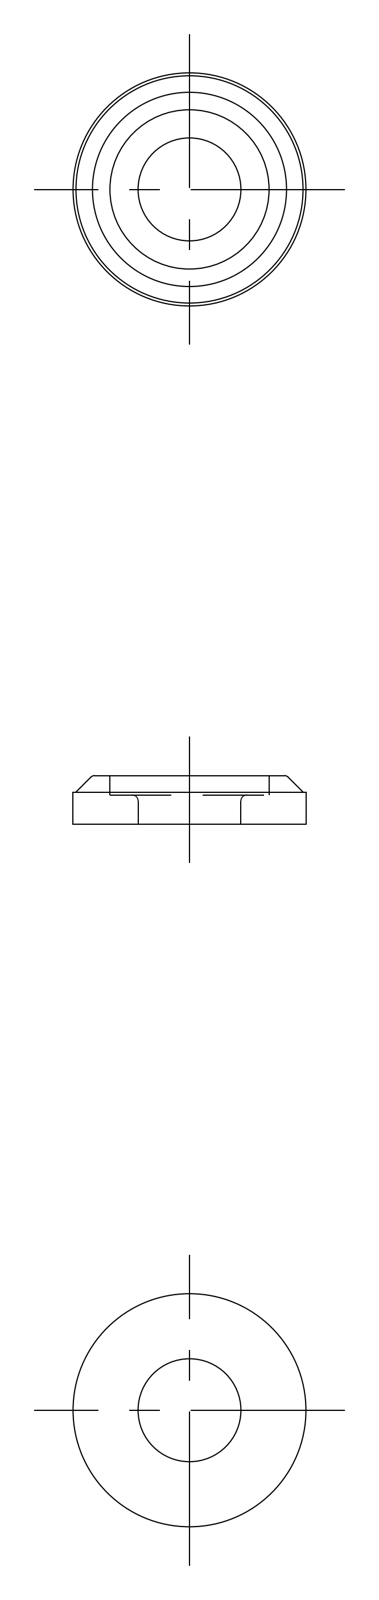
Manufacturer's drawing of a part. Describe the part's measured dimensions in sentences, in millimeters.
The part is named "THA_270_3; facing ring". Its 3-D file was written by "SolidWorks 2015 (AUTOMOTIVE_DESIGN)". It is 1 solid with 16 faces: 4 planar, 6 cylindrical and 6 other. Overall it measures 12 by 12 by 2.5 millimeters. Its volume is 179 cubic millimeters and its surface area 304 square millimeters. Round holes: 1 of diameter 5.3, 1 of diameter 8.2. Round bosses or shafts: 1 of diameter 12. The main face-to-face distances are 1.5, 2.5, 1, 1.65, 0.85.
